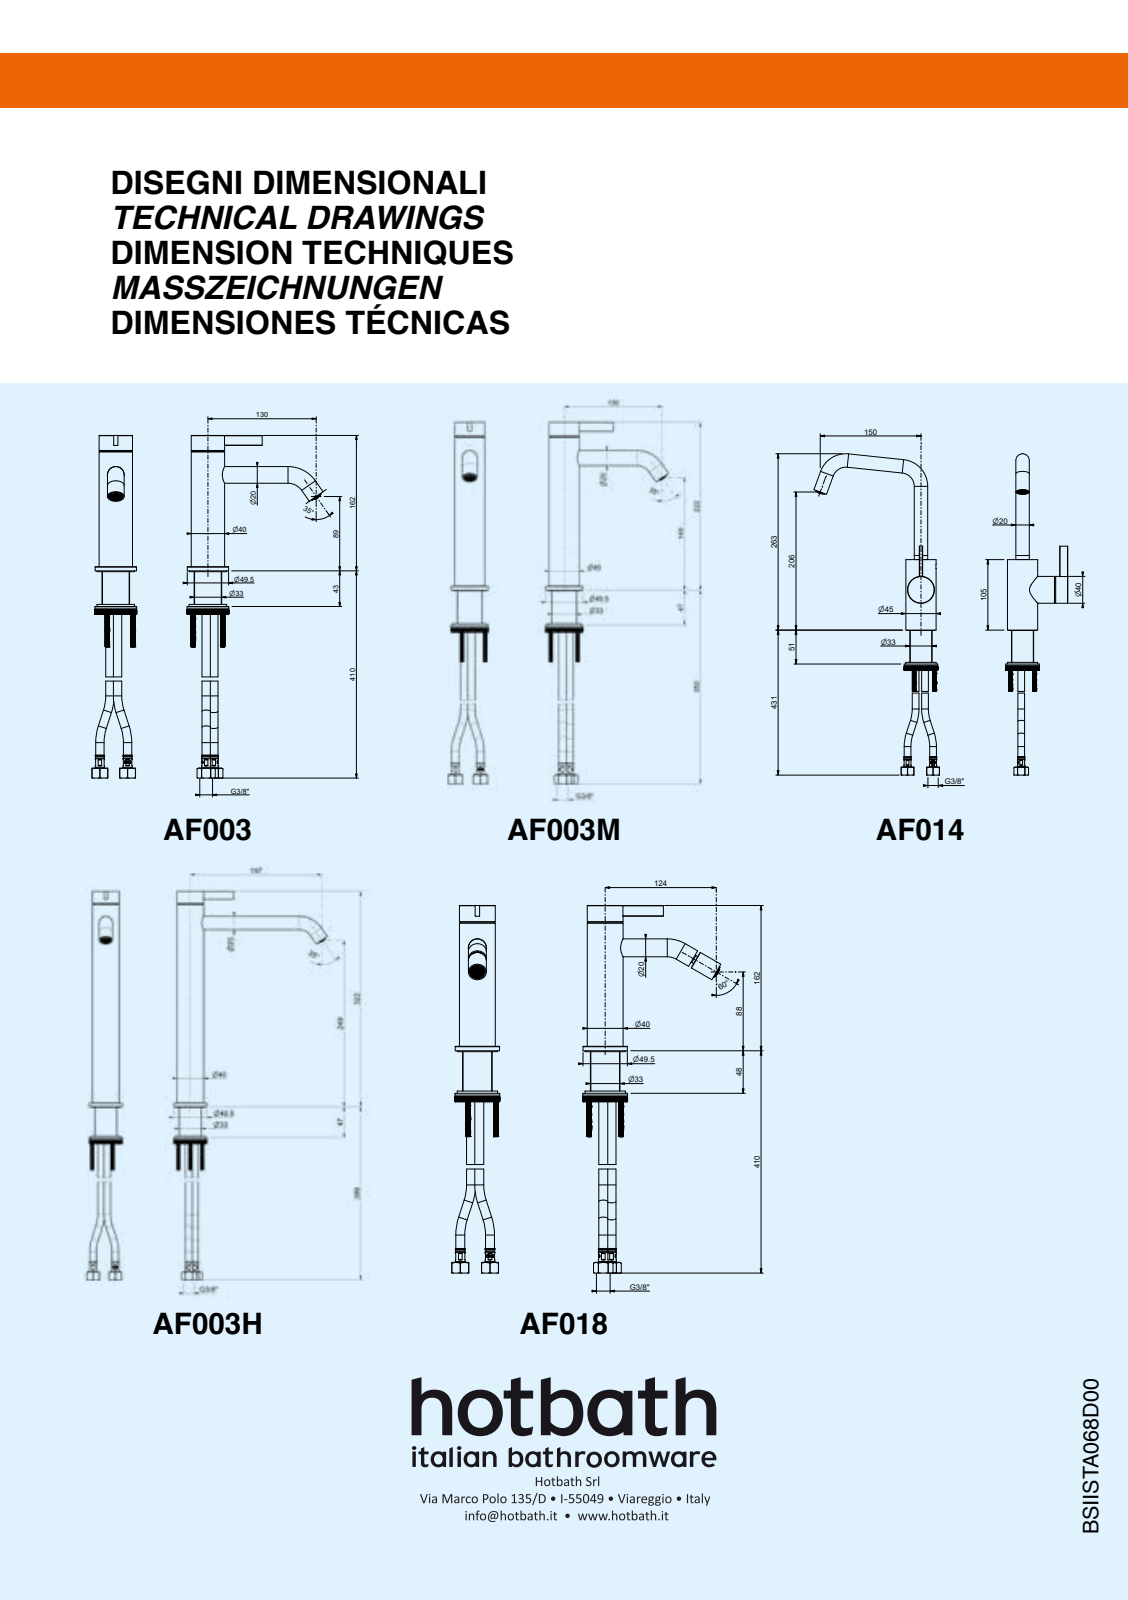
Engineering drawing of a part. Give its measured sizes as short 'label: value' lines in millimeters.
name: AF003-00; ABIX201C003; SARBSA0003_oa_0; SARBSC0003 (+7 more)
written by: Solid Edge (AUTOMOTIVE_DESIGN)
unit: mm
bodies: 7 solids, 2781 faces (1866 planar, 307 cylindrical, 608 other)
size: 162.6 × 162.3 × 49.5
volume: 147 572 mm³; area: 62 381 mm²
holes: 3× ⌀11, 2× ⌀2.5, 2× ⌀3.5, 2× ⌀7.25, 2× ⌀9, 1× ⌀3.2, 1× ⌀6.8, 1× ⌀12, 1× ⌀12.15, 1× ⌀12.45, 1× ⌀13.2, 1× ⌀13.55
bosses: 3× ⌀0.9, 2× ⌀20, 1× ⌀49.5, 1× ⌀38, 1× ⌀37.3, 1× ⌀37, 1× ⌀34.5, 1× ⌀17
rounds: 63× R0.1, 8× R0.2, 8× R0.9, 4× R0.25, 4× R0.4, 4× R0.6, 4× R1.27, 4× R1.3
face distances: 4.6, 5, 152.7, 157.3, 3.5, 156.2, 160.8, 103, 99.5, 53.2
hole spacings: 1.7, 5.94, 7.38, 8.24, 11.3, 11.31, 11.59, 11.93
